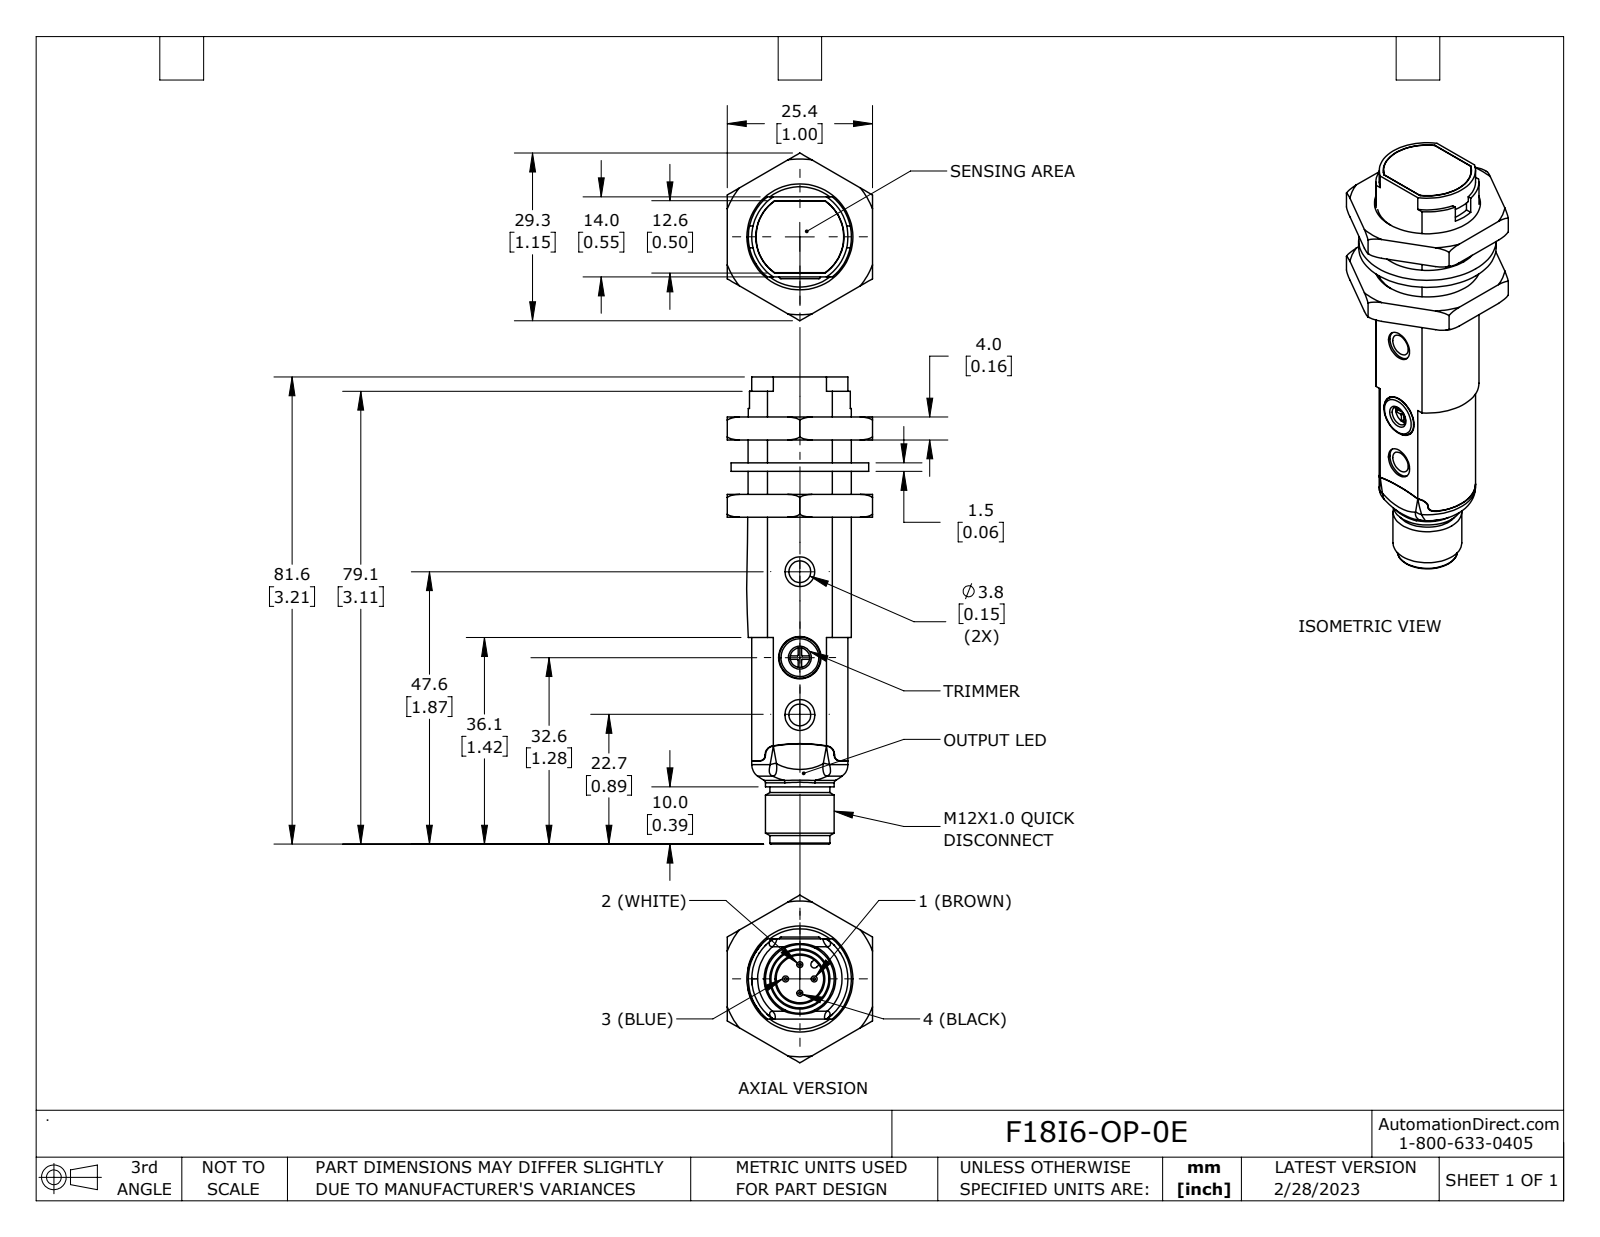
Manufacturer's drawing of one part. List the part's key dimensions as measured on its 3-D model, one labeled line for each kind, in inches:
Part name (STEP PRODUCT): F18I8-BP-0E
STEP written by: SolidWorks 2021 (AUTOMOTIVE_DESIGN)
Units: inches
Bodies: 4 solids, 207 faces (87 planar, 58 cylindrical, 62 other)
Overall size (bounding box): 3.211 × 1.153 × 0.998
Volume: 1.119 in³ · Surface area: 13.02 in²
Round holes (diameter × count): ⌀0.15 ×2, ⌀0.134 ×1, ⌀0.205 ×1, ⌀0.291 ×1, ⌀0.689 ×1, ⌀0.709 ×1
Round bosses / shafts (diameter × count): ⌀0.041 ×4, ⌀0.945 ×1, ⌀0.472 ×1, ⌀0.413 ×1, ⌀0.283 ×1
Partial cylindrical surfaces — rounded edges, fillets, slot ends (radius × count): R0.039 ×4, R0.059 ×4, R0.102 ×2, R1.102 ×2, R0.02 ×1, R0.024 ×1, R0.141 ×1, R0.301 ×1
Main face-to-face distances: 0.157, 0.374, 0.551, 0.531, 0.217, 0.315, 0.998, 0.689, 0.433, 0.059
Hole centre spacings: 0.394, 0.591, 0.984
